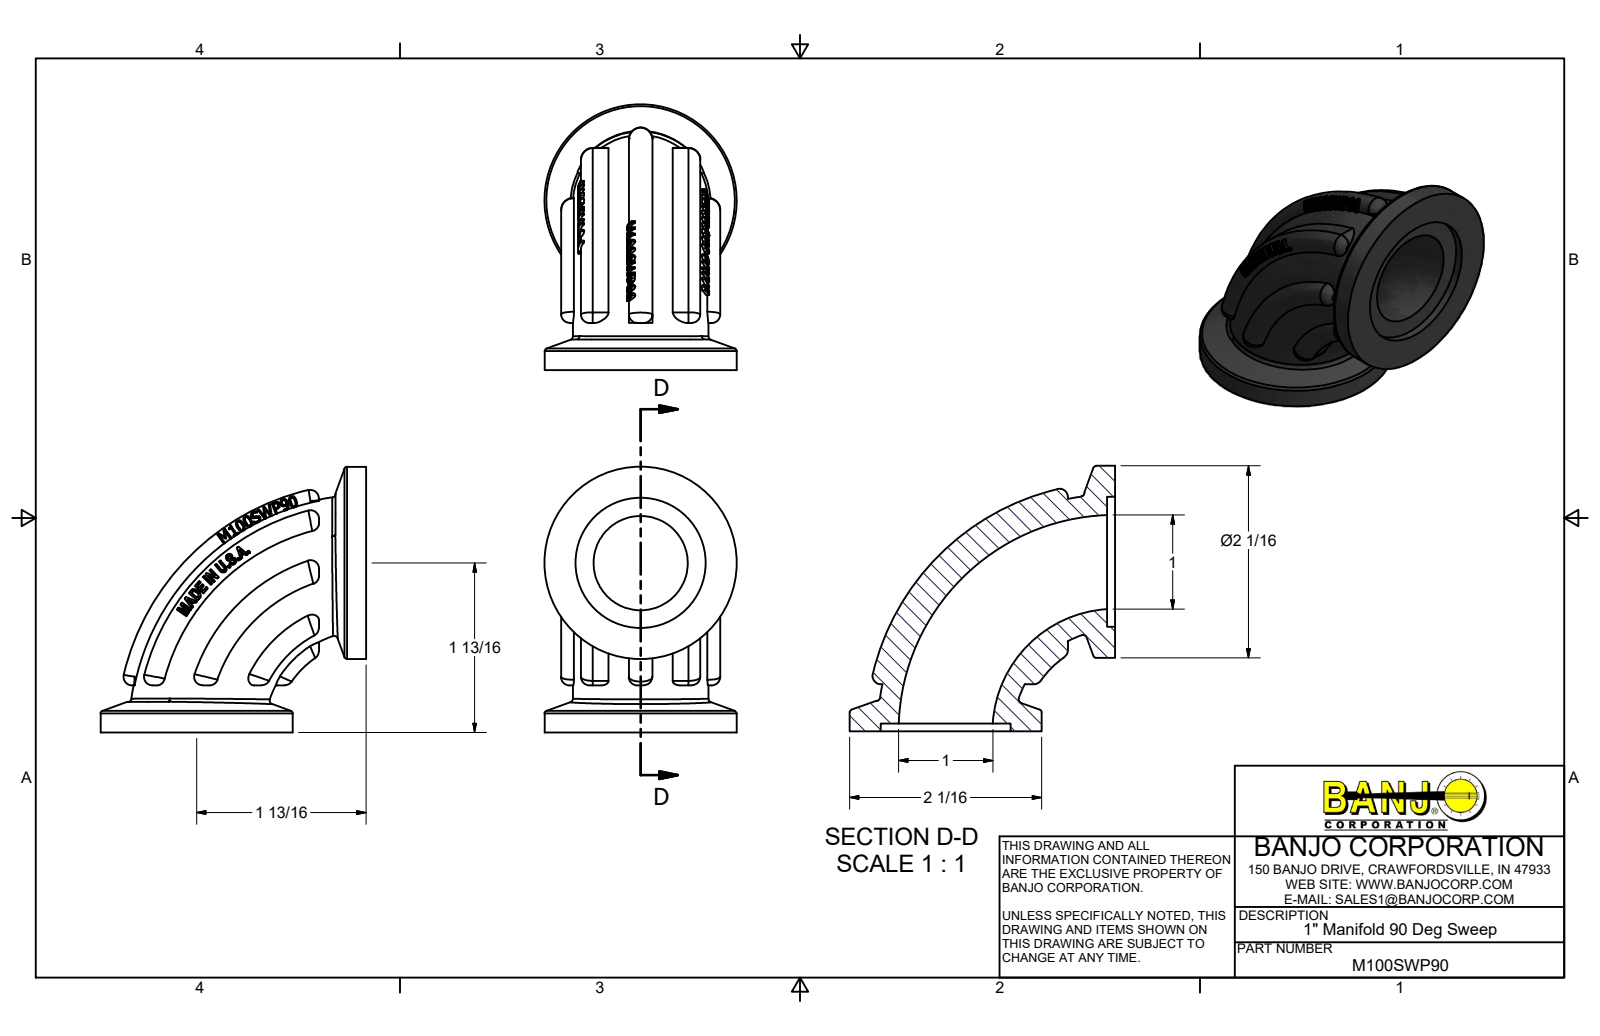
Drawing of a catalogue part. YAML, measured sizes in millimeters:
part_name: "M100SWP90"
step_written_by: "Autodesk Inventor 2017 (AUTOMOTIVE_DESIGN)"
units: millimeters
bodies: {solids: 1, faces: 575, planar: 264, cylindrical: 18, other: 293}
overall_size: [71.63, 71.63, 51.82]
volume: 57926
surface_area: 21258
round_holes:
  - {diameter: 35.05, count: 2}
round_bosses_or_shafts:
  - {diameter: 51.82, count: 2}
partial_cylinders:
  - {radius: 2.29, count: 4}
  - {radius: 17.02, count: 2}
  - {radius: 29.61, count: 1}
  - {radius: 61.83, count: 1}
face_to_face_distances: [2.13, 12.7, 10.57, 0.5, 0.51, 3.05, 0.52, 1.98, 1.48, 8.23]
